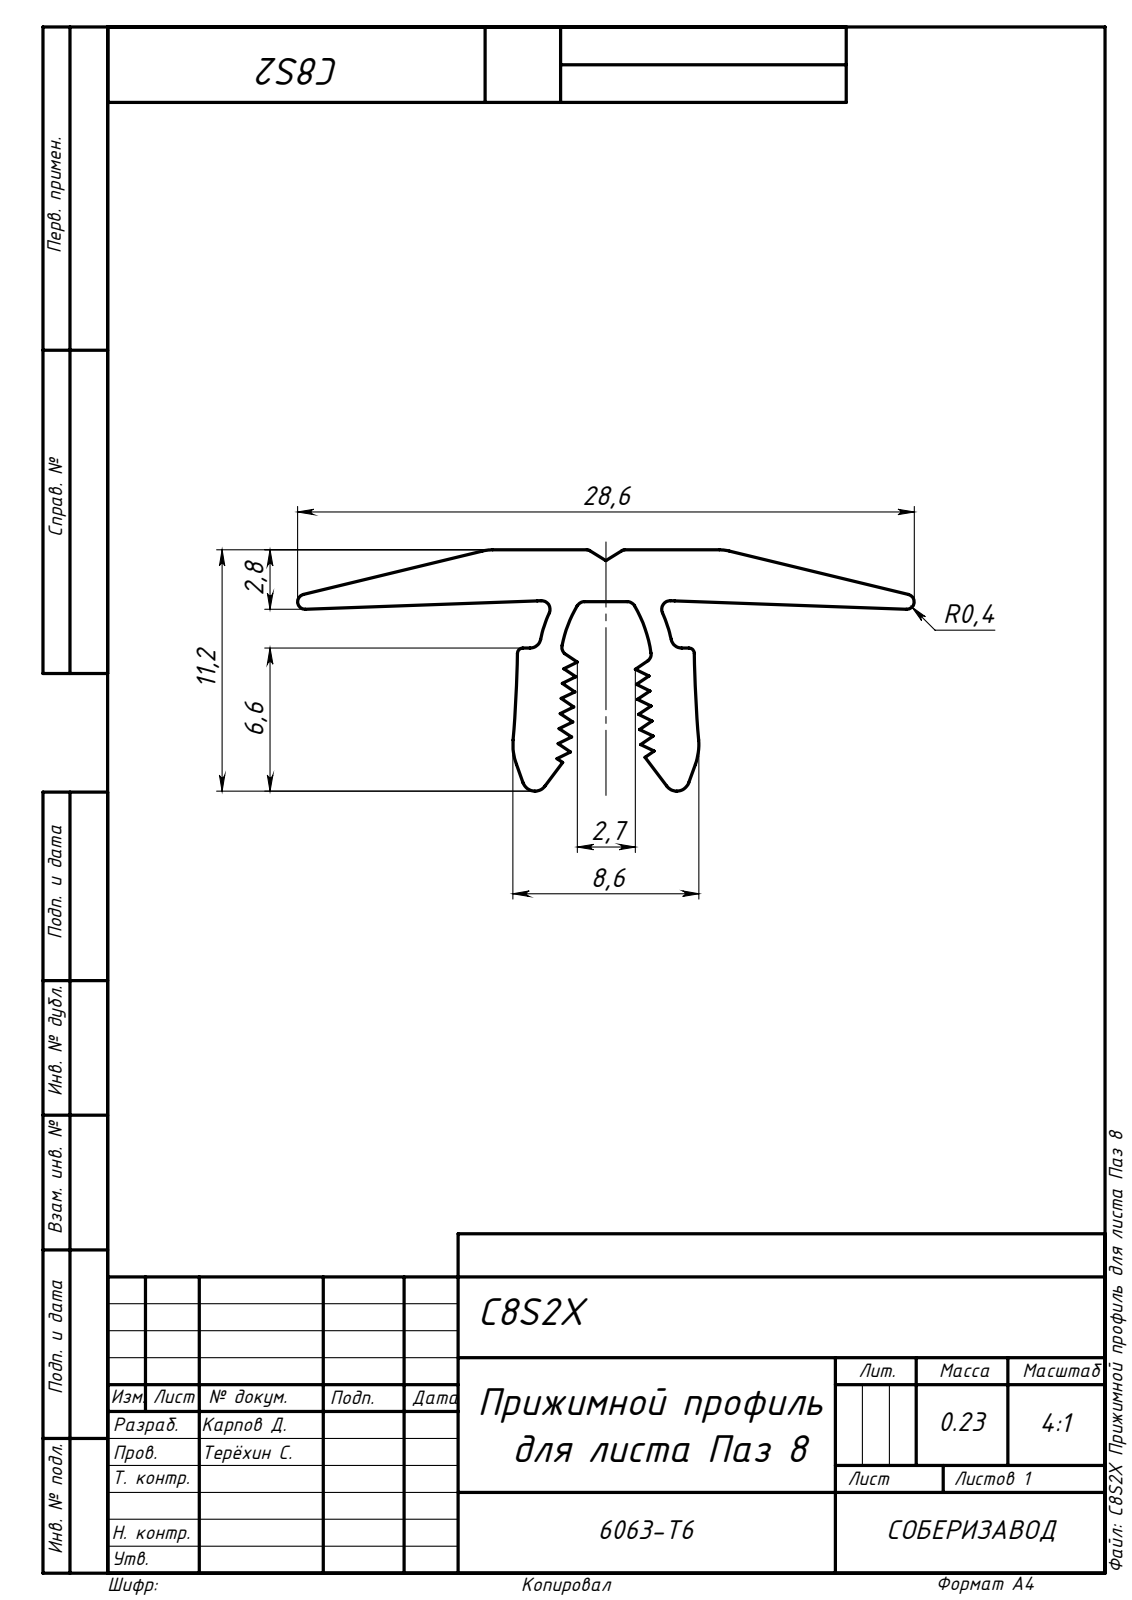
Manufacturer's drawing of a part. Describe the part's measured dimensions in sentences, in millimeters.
The part is named "C8S2X Прижимной профиль для листа Паз 8". Its 3-D file was written by "SolidWorks 2019 (AUTOMOTIVE_DESIGN)". It is 1 solid with 78 faces: 47 planar, 31 cylindrical and 0 other. Overall it measures 120 by 28.6 by 11.2 millimeters. Its volume is 10 433 cubic millimeters and its surface area 12 713 square millimeters. Partial cylindrical surfaces (rounded edges, fillets, slot ends): 6 of radius 0.4, 4 of radius 0.25, 4 of radius 0.6, 4 of radius 6, 2 of radius 0.35, 2 of radius 0.5, 2 of radius 2, 2 of radius 2.7. The main face-to-face distances are 1.21, 0.61, 1.82, 0.6, 2.42, 3.03, 1.22, 2.43, 1.81, 2.4.
